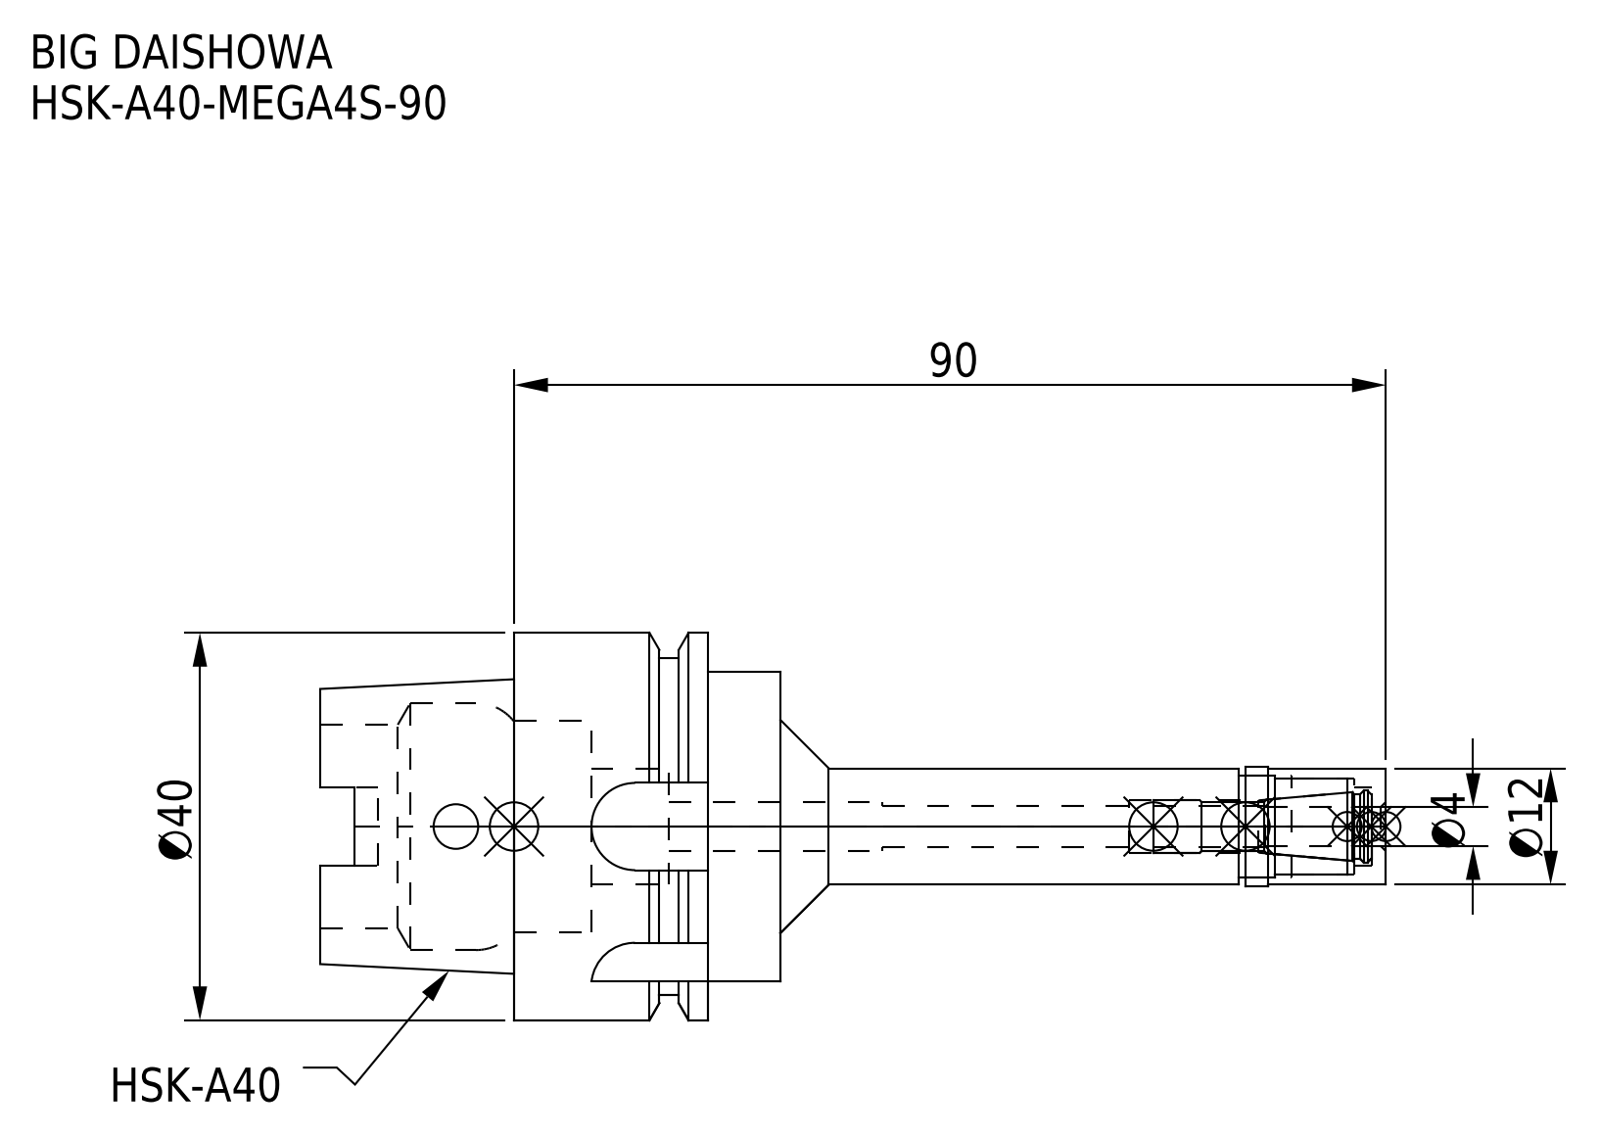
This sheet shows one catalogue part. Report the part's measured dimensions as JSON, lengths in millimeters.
{"part_name": "HSK-A40-MEGA4S-90-040-FreeParts; DXF_TEMP_ASSY_ASM_4_ASM.stp; HSK-A40-MEGA4S-90_1.stp; HSK-A40-MEGA4S-90-040.stp (+3 more)", "step_written_by": "SolidWorks 2019 (CONFIG_CONTROL_DESIGN)", "units": "millimeters", "bodies": {"solids": 2, "faces": 123, "planar": 47, "cylindrical": 56, "other": 20}, "overall_size": [110, 40, 40], "volume_mm3": 36576, "surface_area_mm2": 14552, "round_holes": [[4.1, 1], [4.2, 1], [4.6, 1], [5, 1], [5.4, 1], [8, 1], [10, 1], [10.5, 1], [21, 1], [21.8, 1], [25.5, 1]], "round_bosses_or_shafts": [[40, 1], [34.8, 1], [32, 1], [12.3, 1], [12, 1]], "partial_cylinders_radius": [[1.88, 4], [4.5, 4]], "face_to_face_distances": [20, 27.5, 7.5, 7.95, 19.55, 12.05, 47.5, 40, 27.95, 34]}
